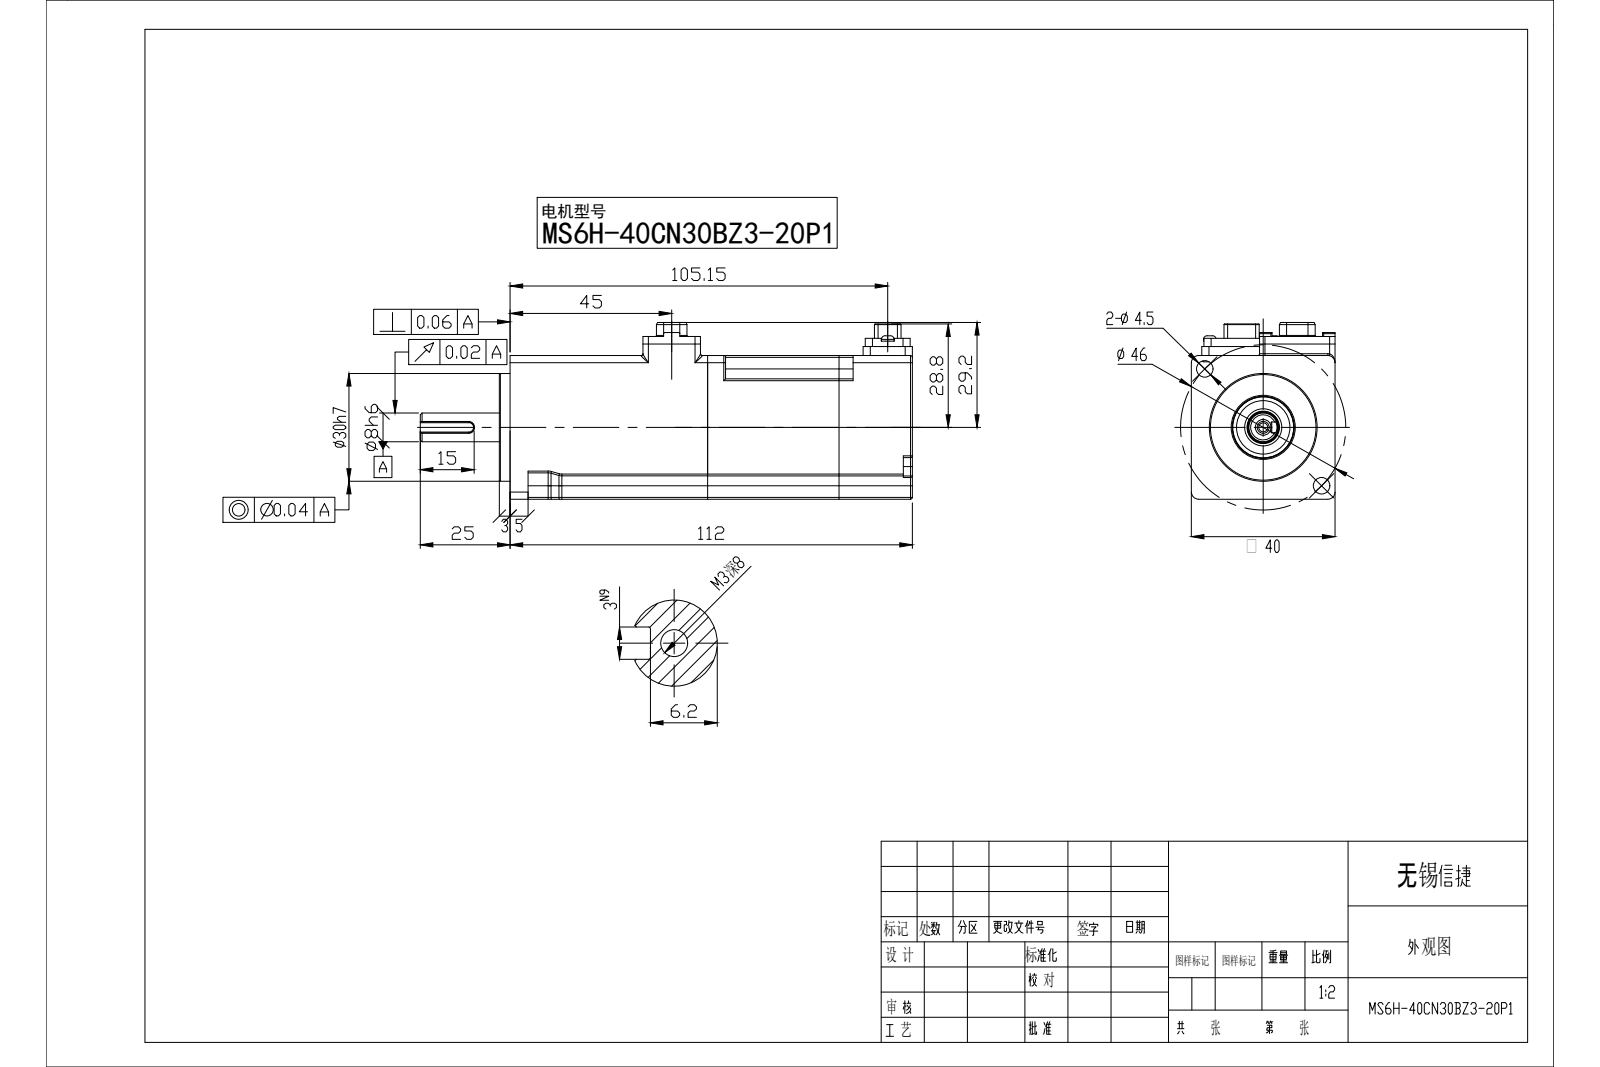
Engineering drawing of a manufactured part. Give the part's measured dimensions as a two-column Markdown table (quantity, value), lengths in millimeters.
| quantity | value |
| --- | --- |
| part name | MS6H-40-CS(M)30BZ3-20P1 |
| STEP written by | SolidWorks 2016 (CONFIG_CONTROL_DESIGN) |
| units | millimeters |
| bodies | 0 solids, 582 faces (275 planar, 216 cylindrical, 91 other) |
| overall size | 137 × 49.2 × 40 |
| round holes (diameter × count) | 2.1 × 8, 2.2 × 4, 1.6 × 2, 2.7 × 2, 4.6 × 2, 2.5 × 1, 9 × 1, 14.86 × 1 |
| round bosses / shafts (diameter × count) | 3.5 × 2, 30 × 1, 17 × 1, 10.34 × 1, 8 × 1 |
| partial cylindrical surfaces (radius × count) | 0.5 × 60, 2 × 16, 0.2 × 14, 0.3 × 10, 3 × 8, 1.5 × 5, 1 × 4, 2.5 × 4 |
| main face-to-face distances | 40, 6.5, 33.5, 112, 27, 3, 115, 2.8, 2.5, 42.5 |
| hole center spacings | 5.48, 5.85, 17.98, 20.6, 23, 27.21, 29.14, 32.52 |
